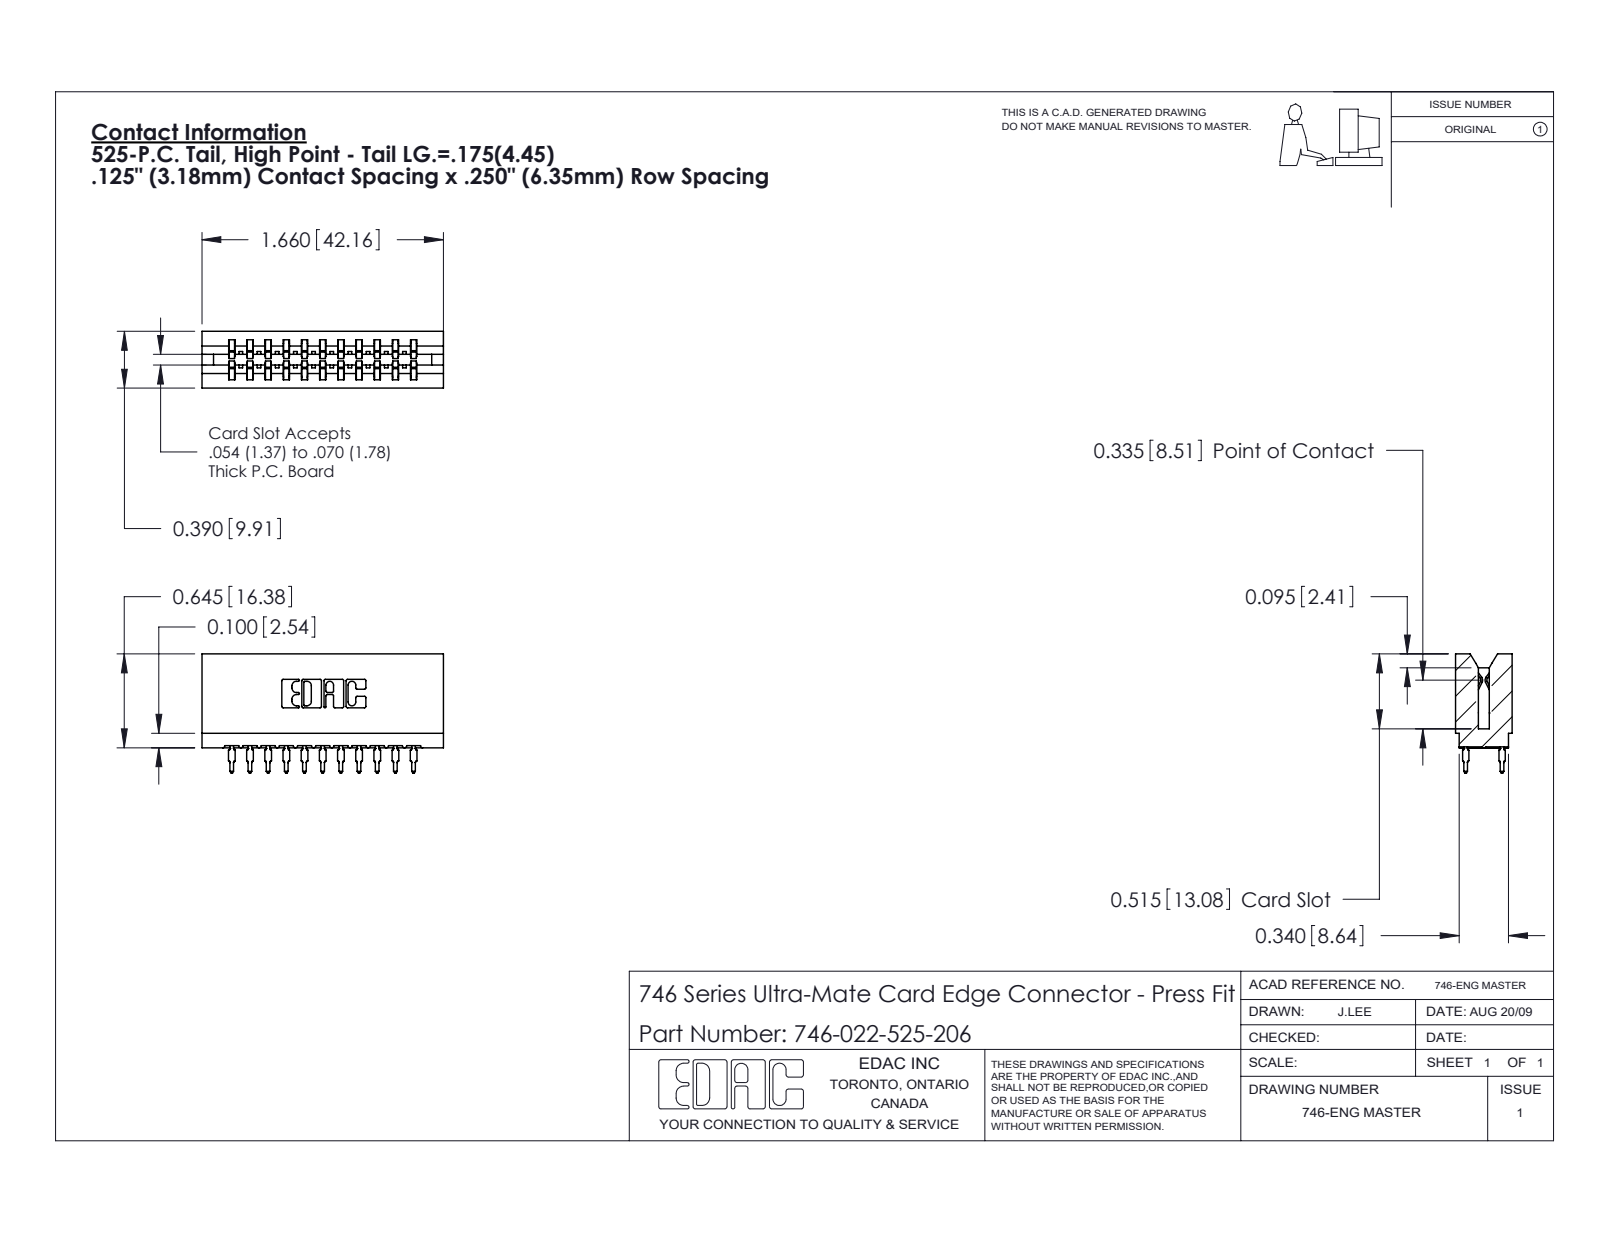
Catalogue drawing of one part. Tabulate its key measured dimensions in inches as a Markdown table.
| quantity | value |
| --- | --- |
| part name | 746-292-001_525; 746 Part_.515 Slot Depth - 06; 746-022-525-206 |
| STEP written by | SolidWorks 2020 (CONFIG_CONTROL_DESIGN) |
| units | inches |
| bodies | 23 solids, 2067 faces (1068 planar, 427 cylindrical, 572 other) |
| overall size | 1.66 × 0.819 × 0.39 |
| volume | 0.286 in³ |
| surface area | 10.64 in² |
| partial cylindrical surfaces (radius × count) | 0.021 × 44, 0.01 × 22, 0.015 × 12, 0.005 × 8, 0.011 × 8, 0.007 × 6, 0.031 × 6, 0.026 × 3 |
| main face-to-face distances | 0.25, 0.333, 0.5, 0.057, 0.125, 0.125, 0.39, 0.042, 0.208, 0.458 |
